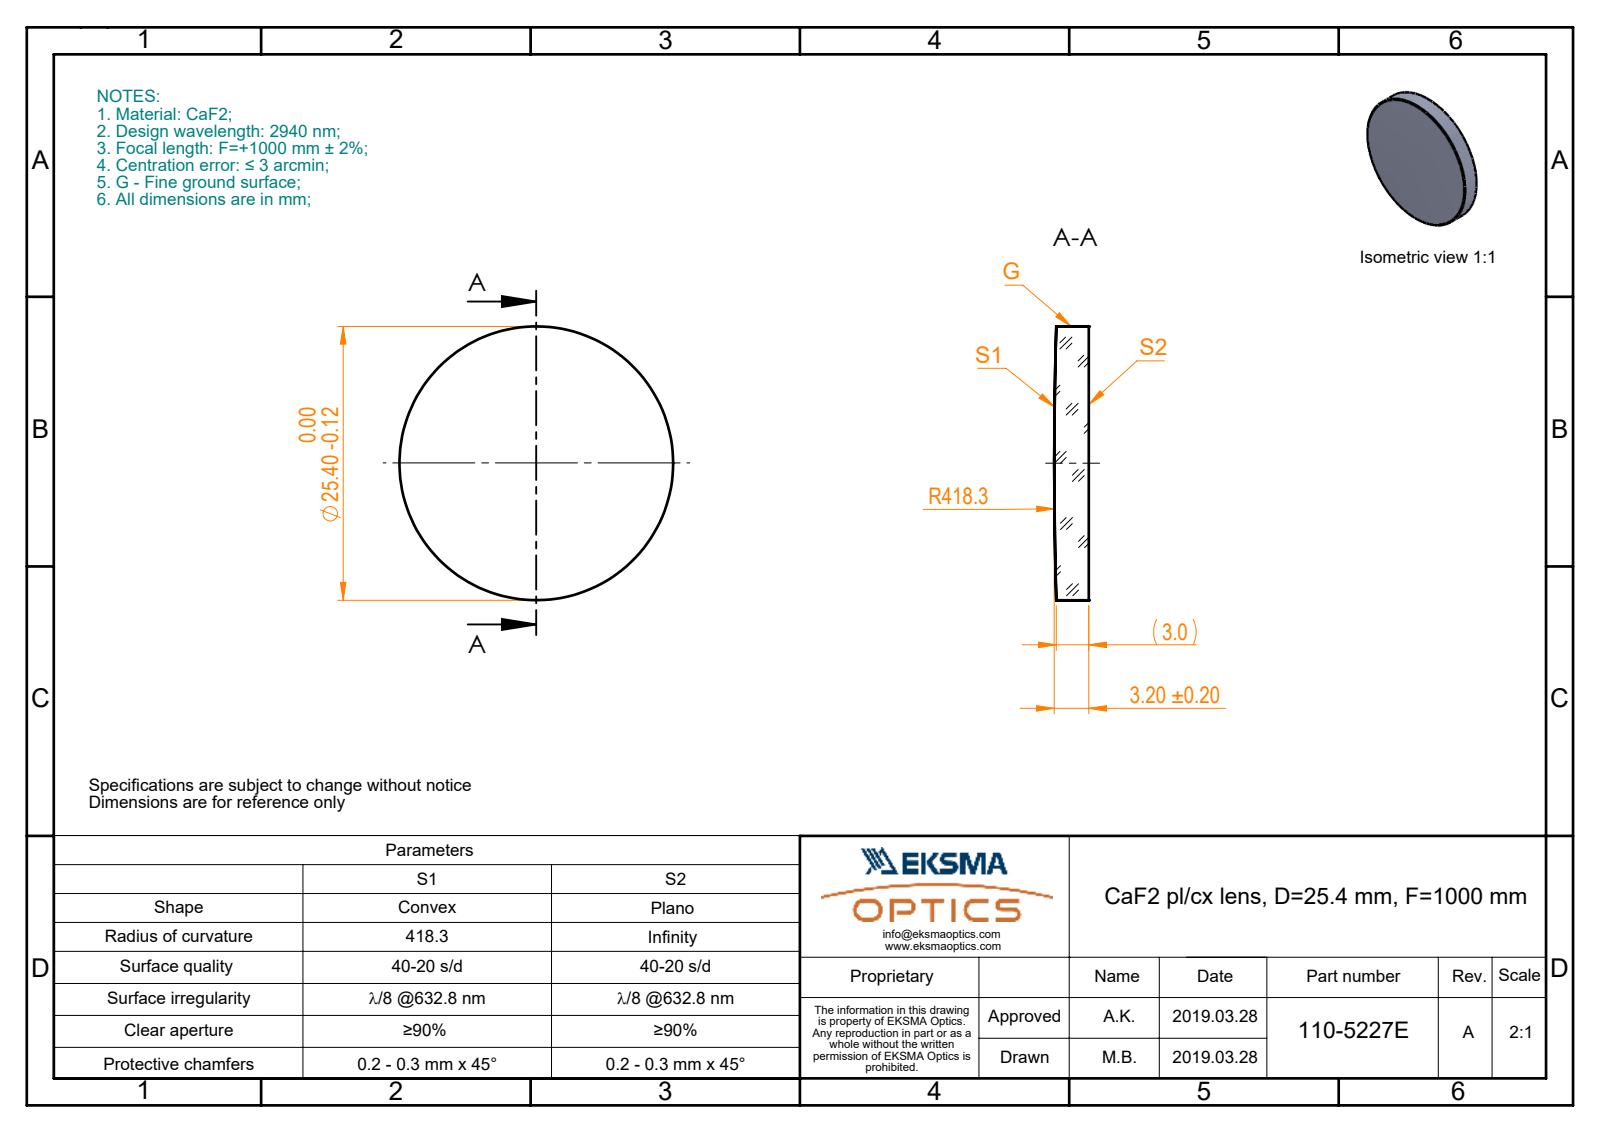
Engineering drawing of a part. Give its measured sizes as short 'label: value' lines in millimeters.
name: 110-5227E CaF2 pl-cx 25.4 F1000
written by: SolidWorks 2017 (CONFIG_CONTROL_DESIGN)
unit: mm
bodies: 1 solid, 5 faces (1 planar, 2 cylindrical, 2 other)
size: 25.4 × 25.4 × 3.2
volume: 1 573 mm³; area: 1 253 mm²
bosses: 1× ⌀25.4
